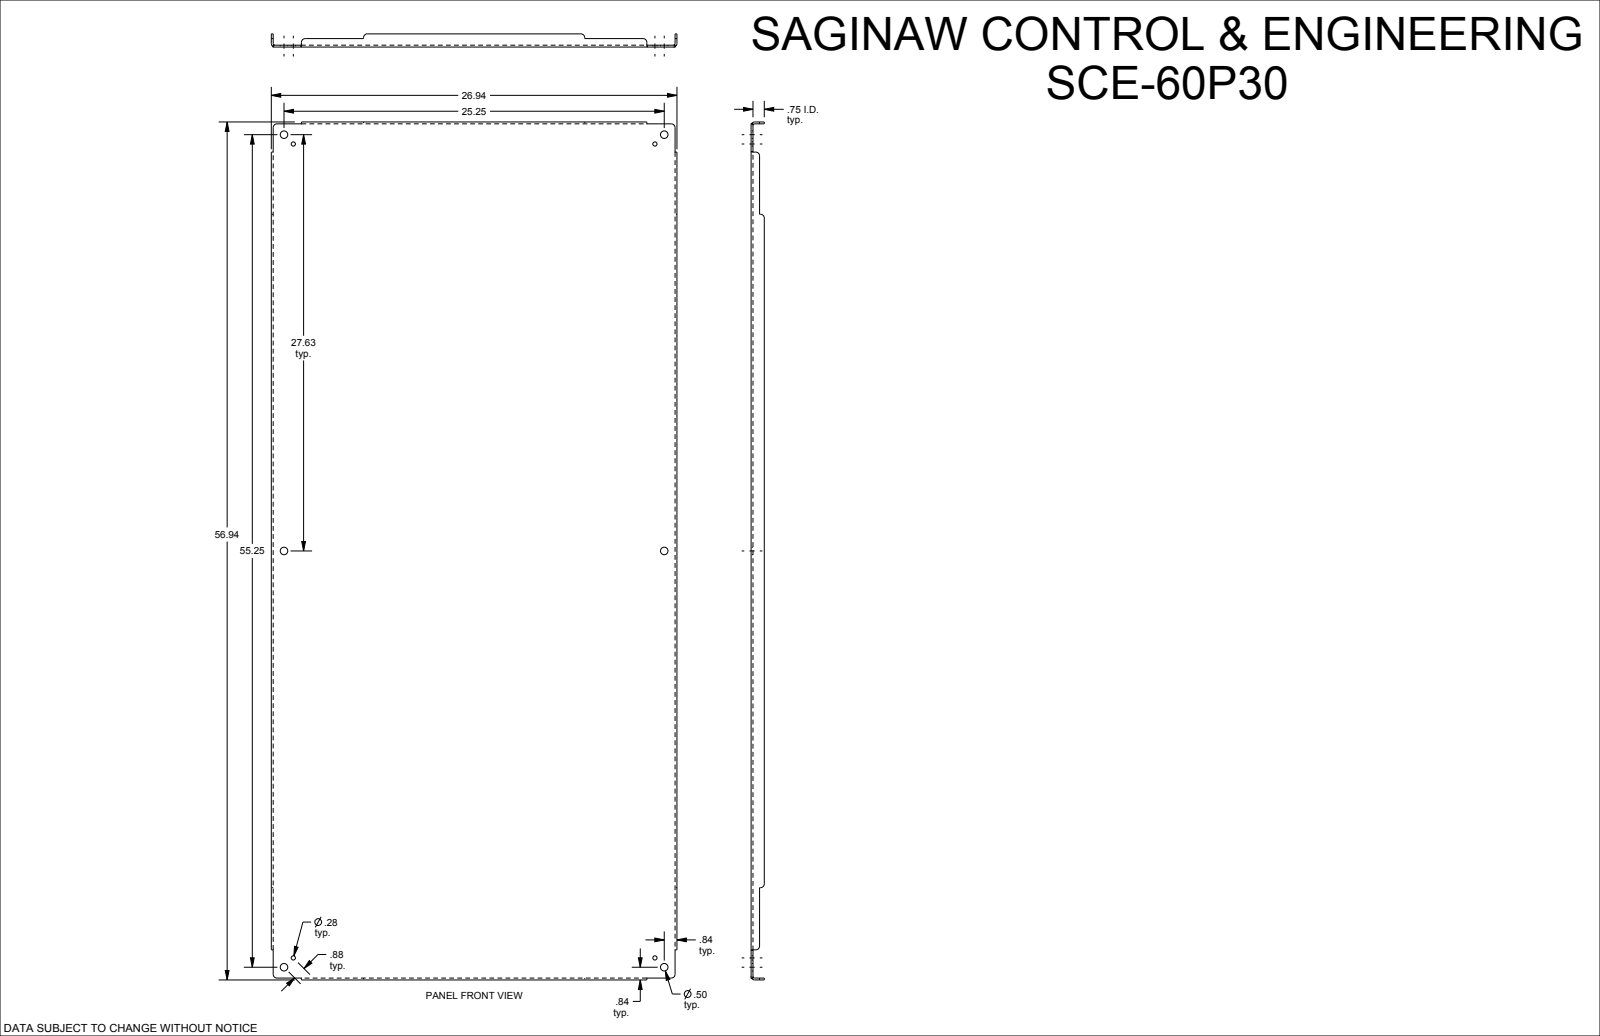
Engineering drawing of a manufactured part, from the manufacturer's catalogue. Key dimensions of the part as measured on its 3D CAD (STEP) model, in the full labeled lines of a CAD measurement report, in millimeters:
Part name (STEP PRODUCT): SCE-60P30
STEP written by: SolidWorks 2019 (CONFIG_CONTROL_DESIGN)
Units: millimetres
Bodies: 1 solid, 108 faces (46 planar, 38 cylindrical, 24 other)
Overall size (bounding box): 1446.2 × 684.2 × 22.2
Volume: 3 323 000 mm³ · Surface area: 2 108 000 mm²
Round holes (diameter × count): ⌀12.7 ×6, ⌀7.1 ×4
Partial cylindrical surfaces — rounded edges, fillets, slot ends (radius × count): R6.4 ×12, R2.8 ×4, R6 ×4
Main face-to-face distances: 3.2, 3.2, 681.1, 677.8, 684.2, 1443.1, 19.1, 22.2, 1439.8, 1446.2
Hole centre spacings: 22.2, 625.8, 686.1, 701.7, 928.4, 950.6, 1387.7, 1522.1
